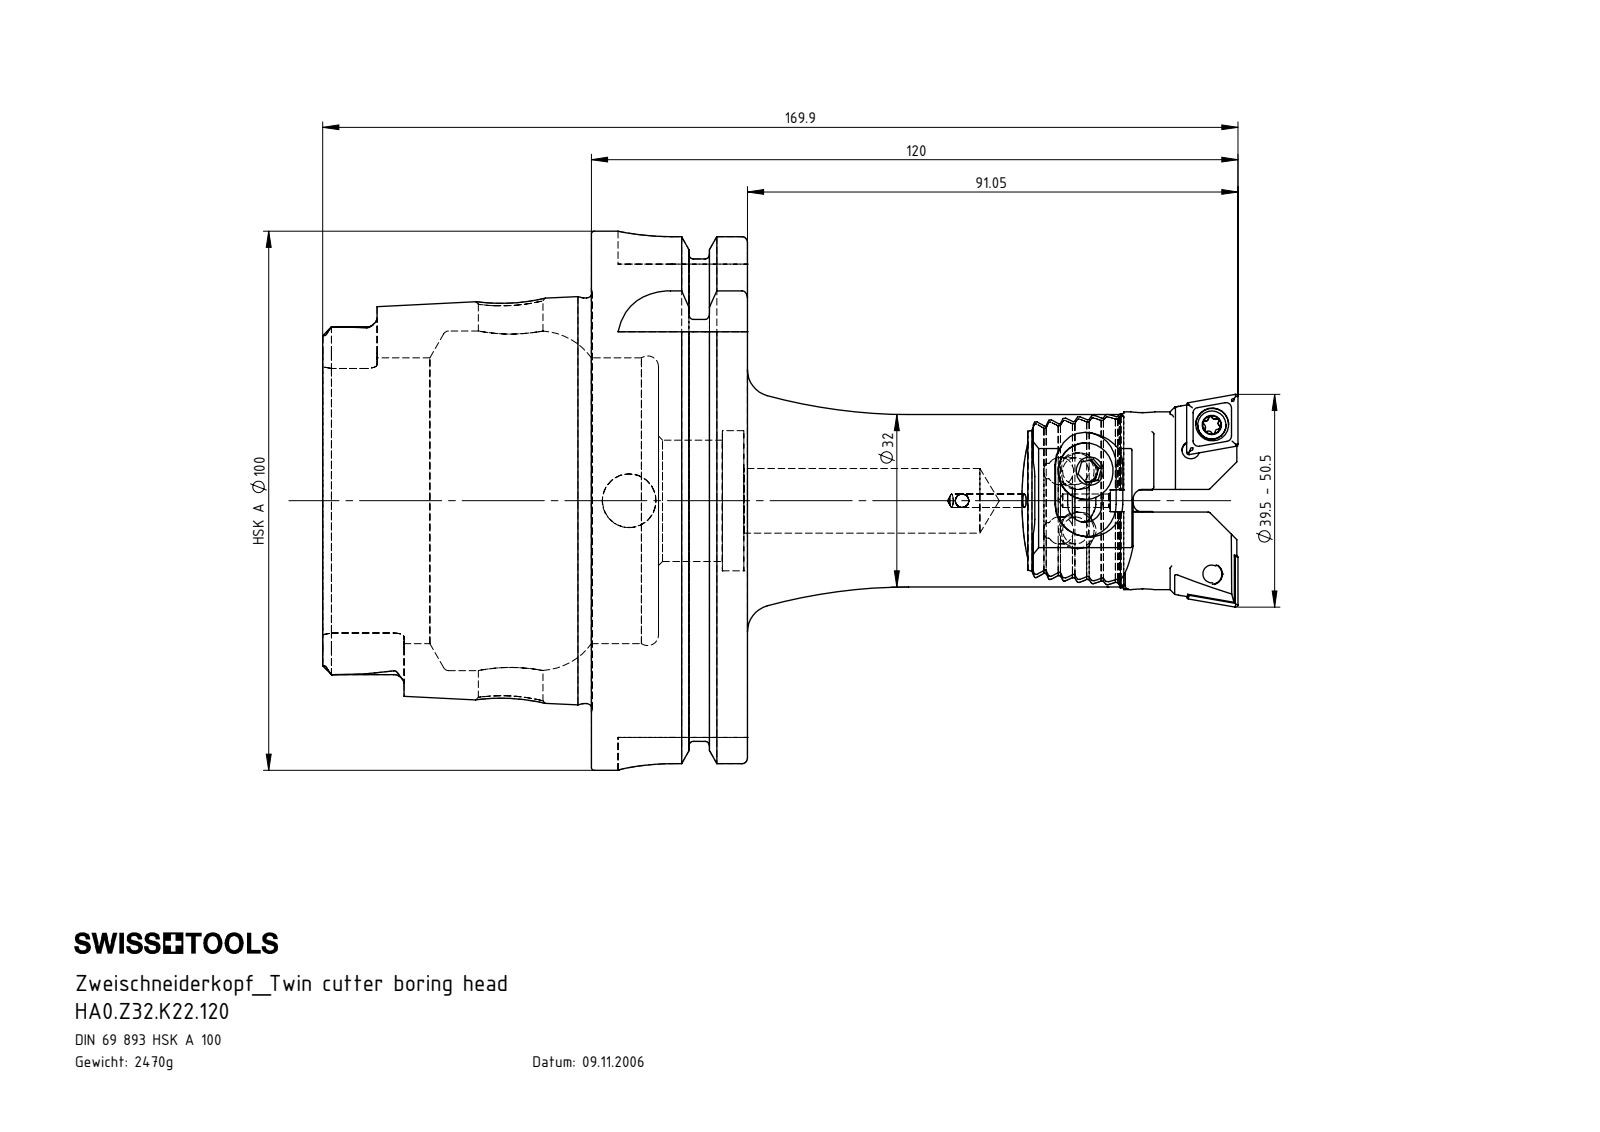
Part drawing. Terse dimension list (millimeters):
name: Z32-WCB.001.021; CCMT09T304; Z32-ER3.001.013_A; HA0-Z32.K21.120_A_Fertigbearbeitung (+5 more)
written by: SolidWorks 2022 (CONFIG_CONTROL_DESIGN)
unit: mm
bodies: 11 solids, 841 faces (339 planar, 245 cylindrical, 257 other)
size: 169.9 × 100 × 100
volume: 314 588 mm³; area: 68 118 mm²
holes: 4× ⌀2.5, 4× ⌀3.3, 2× ⌀1.6, 2× ⌀4.4, 2× ⌀5, 2× ⌀6.1, 2× ⌀6.8, 2× ⌀12, 1× ⌀2, 1× ⌀3.5, 1× ⌀10, 1× ⌀22.5
bosses: 3× ⌀4, 2× ⌀10.5, 2× ⌀6, 2× ⌀5.25, 1× ⌀100, 1× ⌀91.95, 1× ⌀75.26, 1× ⌀32
rounds: 16× R0.5, 14× R0.2, 12× R0.2, 12× R0.34, 12× R0.59, 6× R1.9, 4× R2, 4× R3.3
face distances: 28.95, 16.5, 12.45, 2.38, 49.9, 62.35, 78.85, 4.76, 9.53, 2.42
hole spacings: 6.07, 6.19, 9, 24.23, 24.33, 28.65, 120, 17.38
